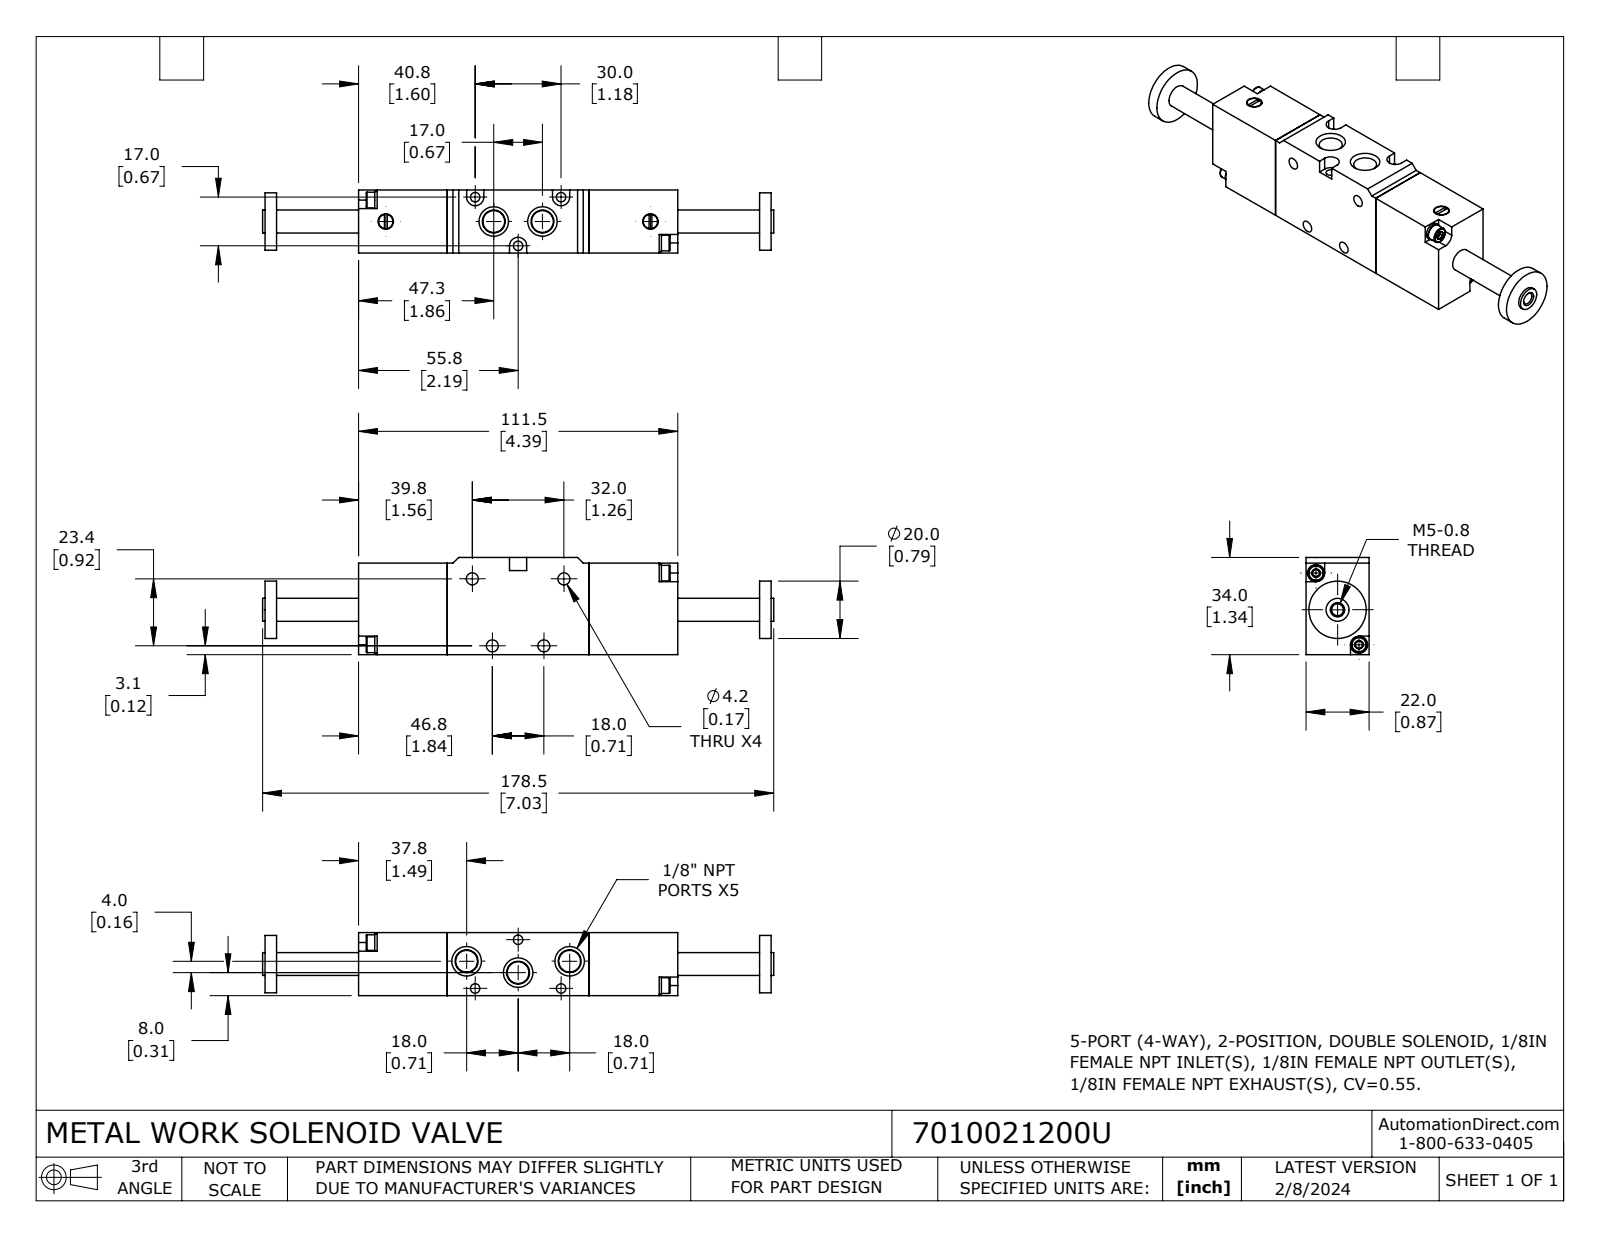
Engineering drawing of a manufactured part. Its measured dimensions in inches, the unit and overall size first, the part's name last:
Units: inches
Overall size (bounding box): 7.028 × 1.339 × 0.866
Round holes (diameter × count): ⌀0.118 ×4, ⌀0.165 ×4, ⌀0.13 ×3, ⌀0.213 ×2, ⌀0.163 ×1
Round bosses / shafts (diameter × count): ⌀0.236 ×4, ⌀0.217 ×4, ⌀0.197 ×2, ⌀0.787 ×1, ⌀0.315 ×1
Partial cylindrical surfaces — rounded edges, fillets, slot ends (radius × count): R0.118 ×3
Main face-to-face distances: 0.866, 1.949, 1.26, 1.22, 3.169, 1.339, 0.079, 4.39, 0.157, 1.283
Hole centre spacings: 0.564, 0.584, 0.591, 0.893, 0.961, 0.984, 1.148, 1.274
Volume: 4.946 in³ · Surface area: 36.62 in²
Bodies: 11 solids, 295 faces (134 planar, 81 cylindrical, 80 other)
Part name (STEP PRODUCT): 7010021200U
STEP written by: SolidWorks 2023 (CONFIG_CONTROL_DESIGN)
